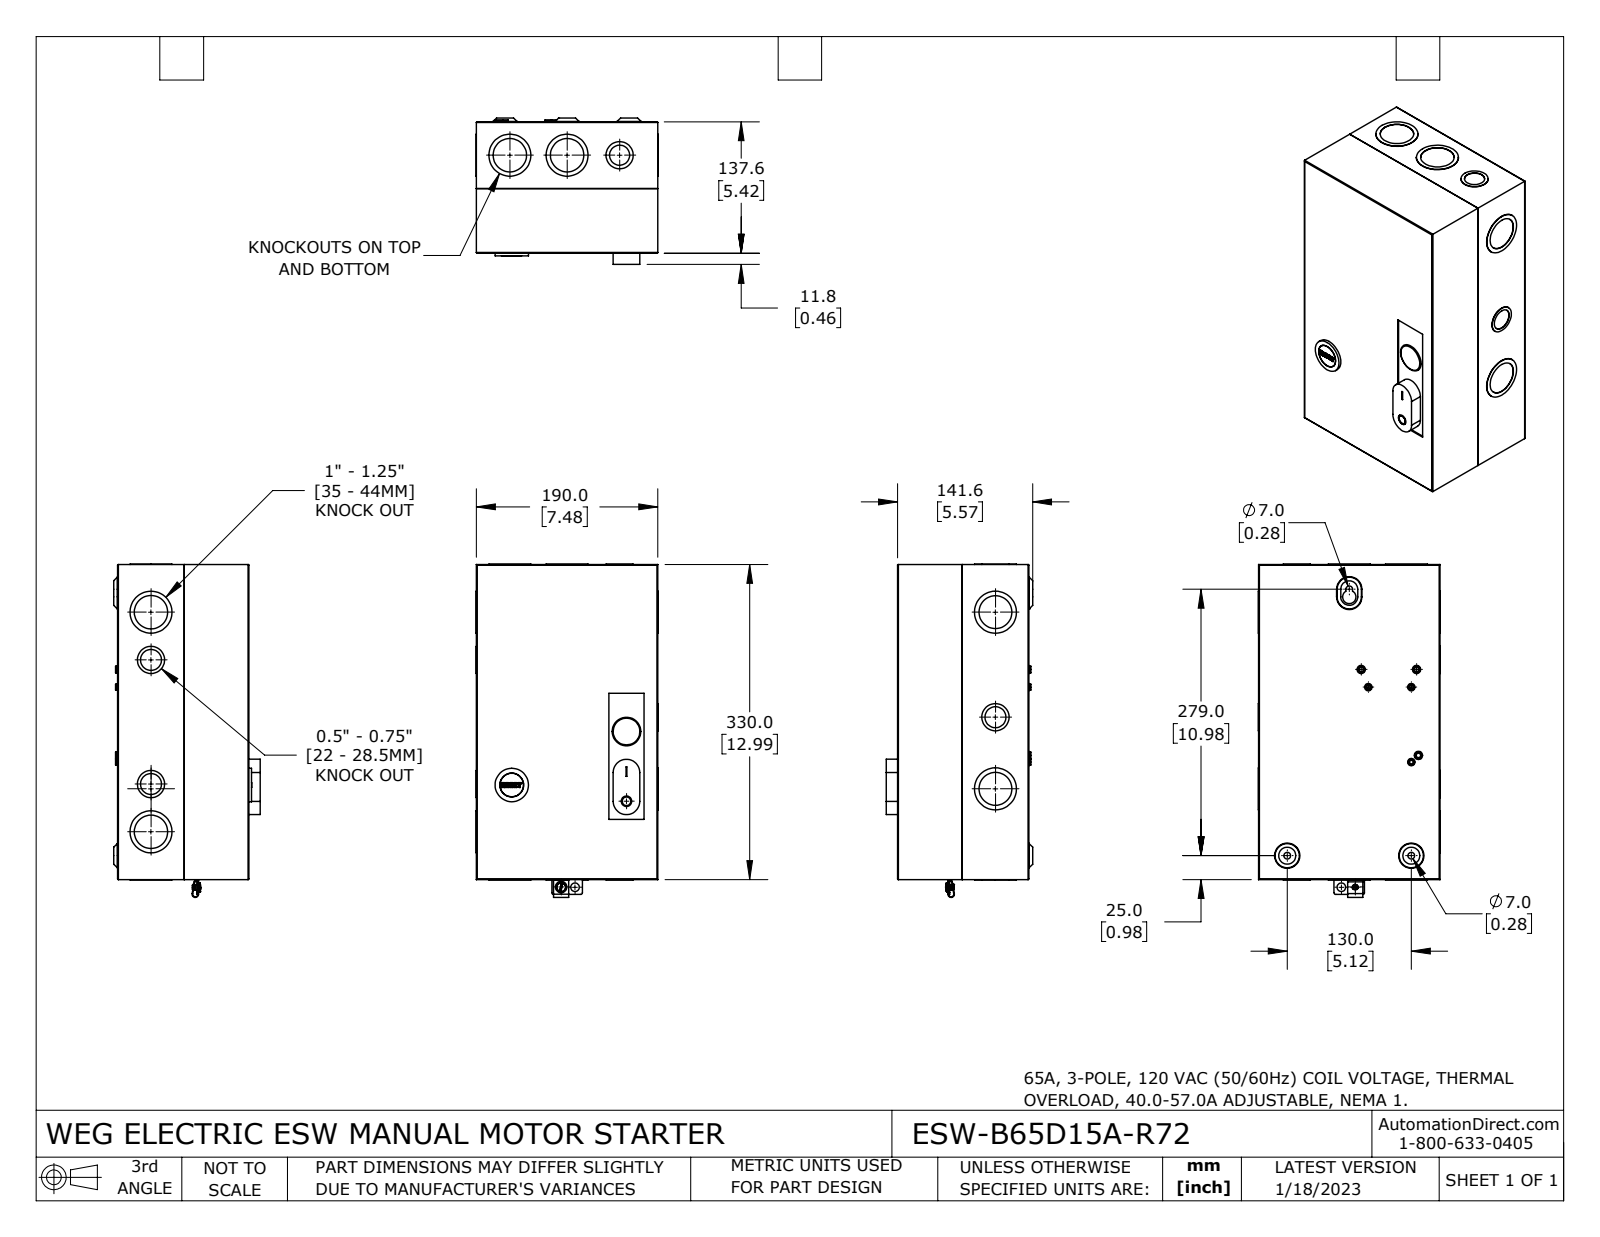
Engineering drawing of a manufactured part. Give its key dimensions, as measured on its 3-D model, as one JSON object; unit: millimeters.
{"part_name": "ESW-B65D15A-R72", "step_written_by": "SolidWorks 2021 (CONFIG_CONTROL_DESIGN)", "units": "millimeters", "bodies": {"solids": 7, "faces": 435, "planar": 161, "cylindrical": 221, "other": 53}, "overall_size": [349, 190.6, 153.4], "volume_mm3": 402800, "surface_area_mm2": 604300, "round_holes": [[35, 4], [3.7, 3], [4.6, 3], [7, 2], [22, 2], [22.5, 2], [34.5, 2], [6.5, 1], [7.1, 1], [9, 1], [11, 1], [11.9, 1]], "round_bosses_or_shafts": [[44, 4], [28.5, 3], [7.1, 3], [6.1, 3], [44, 2], [35, 1], [30.3, 1], [29.2, 1]], "partial_cylinders_radius": [[0.1, 34], [0.8, 8], [2, 3], [3.5, 3], [1.5, 2], [1.9, 2], [2.7, 2], [3.1, 2]], "face_to_face_distances": [1.2, 136.4, 188.8, 135.2, 137.6, 328.8, 187.6, 190, 1.8, 327.6], "hole_center_spacings": [14.5, 45, 50, 58, 60, 130, 180, 278.7]}
